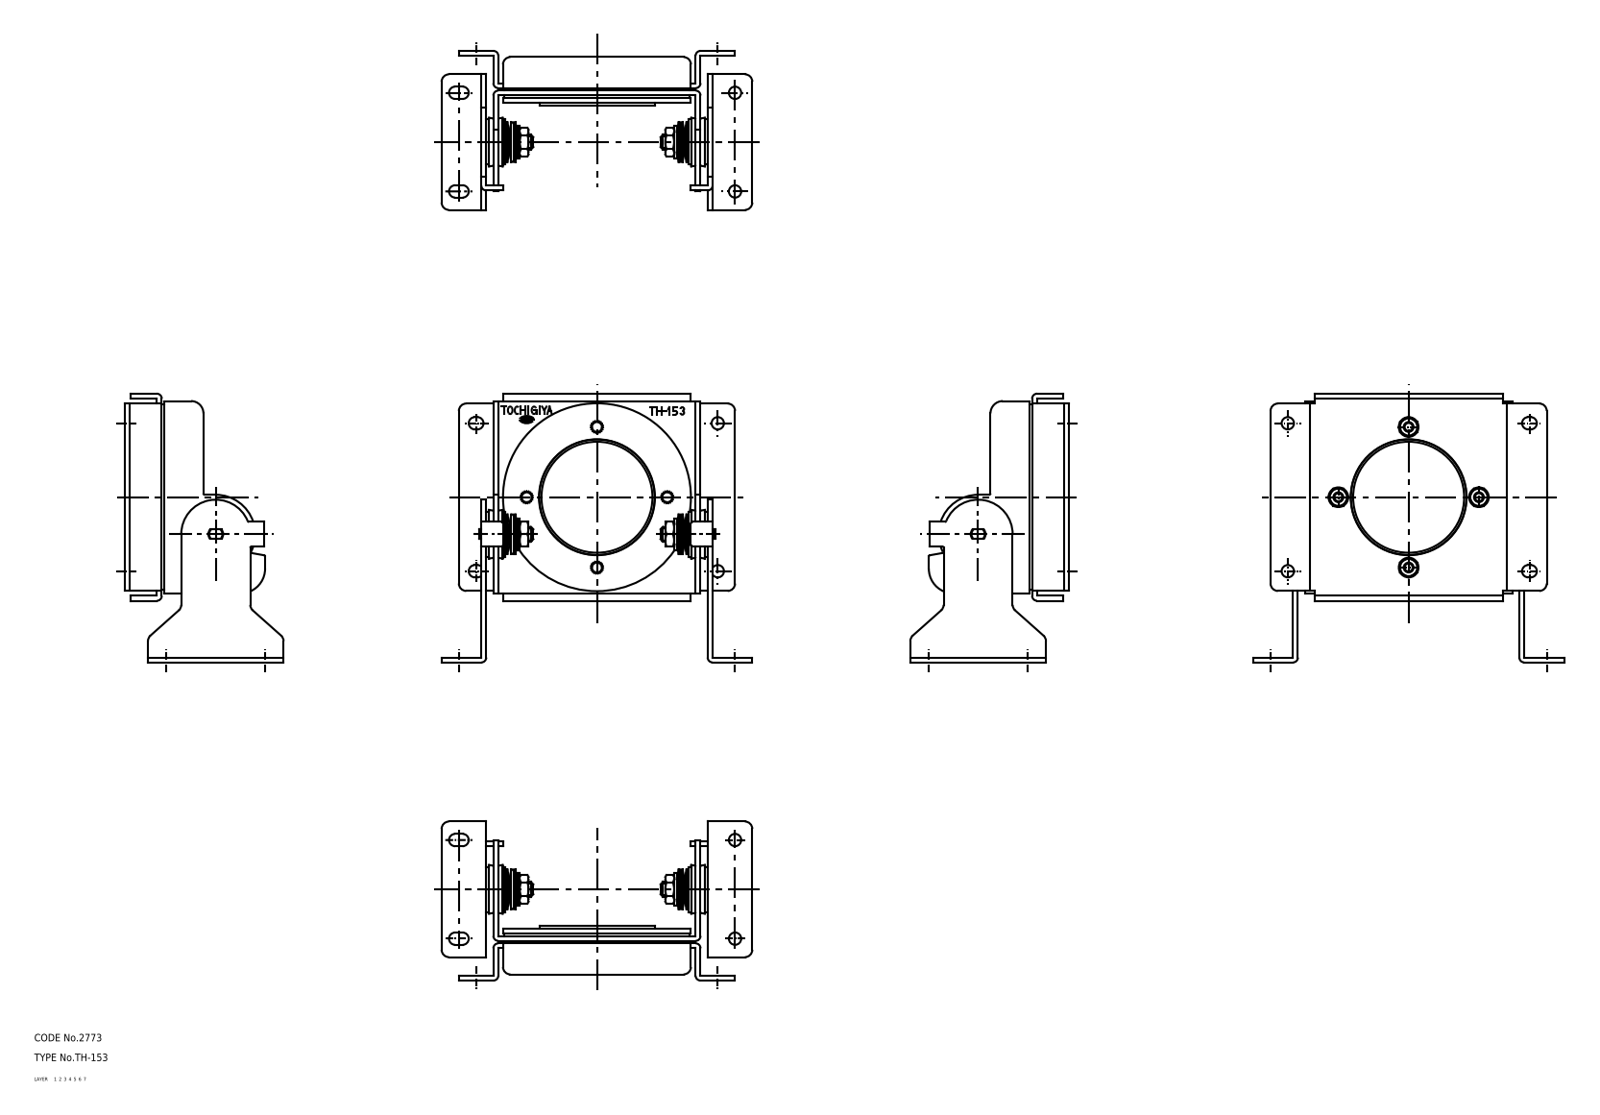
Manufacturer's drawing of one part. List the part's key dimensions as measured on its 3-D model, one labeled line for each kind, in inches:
Part name (STEP PRODUCT): 67140894; 67140907; 67140920; 67140933 (+2 more)
STEP written by: CADfix (AUTOMOTIVE_DESIGN)
Units: inches
Bodies: 6 solids, 717 faces (0 planar, 0 cylindrical, 717 other)
Overall size (bounding box): 4.961 × 4.291 × 2.539
Volume: 4.272 in³ · Surface area: 97.93 in²
